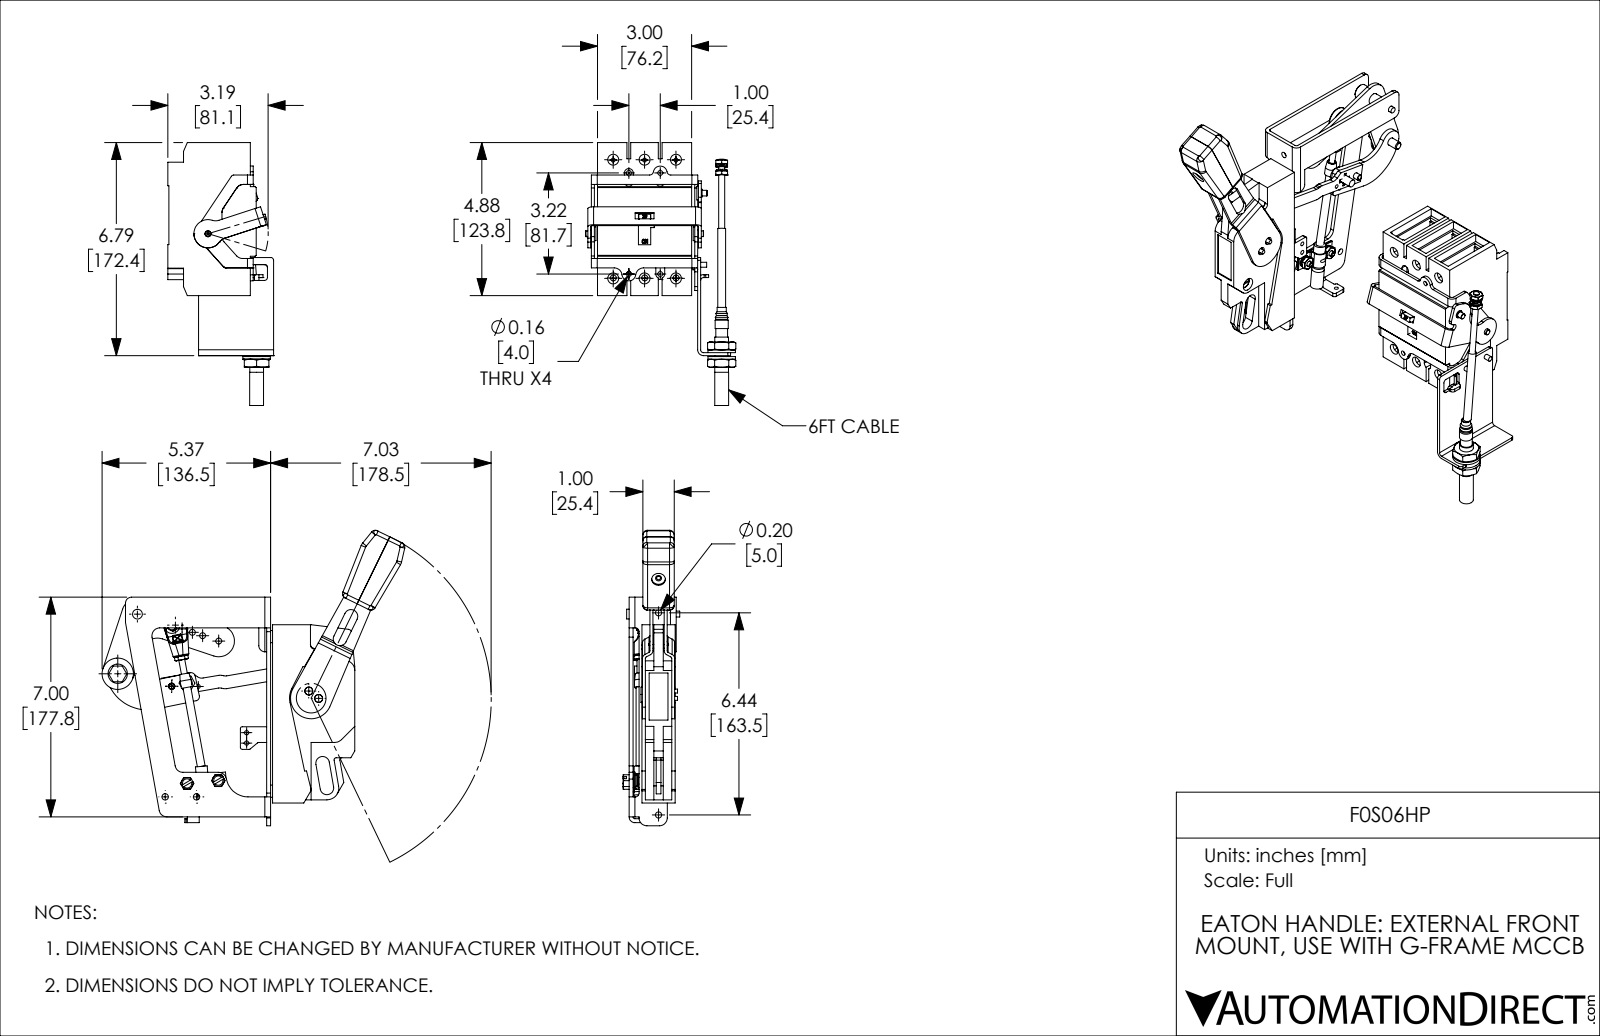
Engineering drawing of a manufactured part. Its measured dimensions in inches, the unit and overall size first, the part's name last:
Units: inches
Overall size (bounding box): 11.71 × 10.066 × 9.651
Round holes (diameter × count): ⌀0.156 ×8, ⌀0.188 ×8, ⌀0.203 ×6, ⌀0.348 ×6, ⌀0.19 ×5, ⌀0.125 ×3, ⌀0.125 ×3, ⌀0.194 ×3, ⌀0.196 ×3, ⌀0.25 ×3, ⌀0.253 ×3, ⌀0.136 ×2
Round bosses / shafts (diameter × count): ⌀0.25 ×9, ⌀0.375 ×5, ⌀0.44 ×4, ⌀0.375 ×3, ⌀0.344 ×3, ⌀0.312 ×3, ⌀0.243 ×3, ⌀0.181 ×3
Partial cylindrical surfaces — rounded edges, fillets, slot ends (radius × count): R0.25 ×31, R0.09 ×23, R0.062 ×17, R0.125 ×17, R0.02 ×12, R0.15 ×12, R0.032 ×11, R0.031 ×10
Main face-to-face distances: 0.094, 0.125, 0.594, 5.342, 8.342, 3, 5.467, 8.467, 0.187, 0.11
Hole centre spacings: 1, 2, 0.017, 0.647, 3.396, 3.663, 3.9, 5.57
Volume: 51.14 in³ · Surface area: 437.6 in²
Bodies: 77 solids, 2152 faces (1122 planar, 779 cylindrical, 251 other)
Part name (STEP PRODUCT): F0S06HP_HANDLE; F0S06HP_BREAKER; F0S06HP
STEP written by: SolidWorks 2019 (CONFIG_CONTROL_DESIGN)
